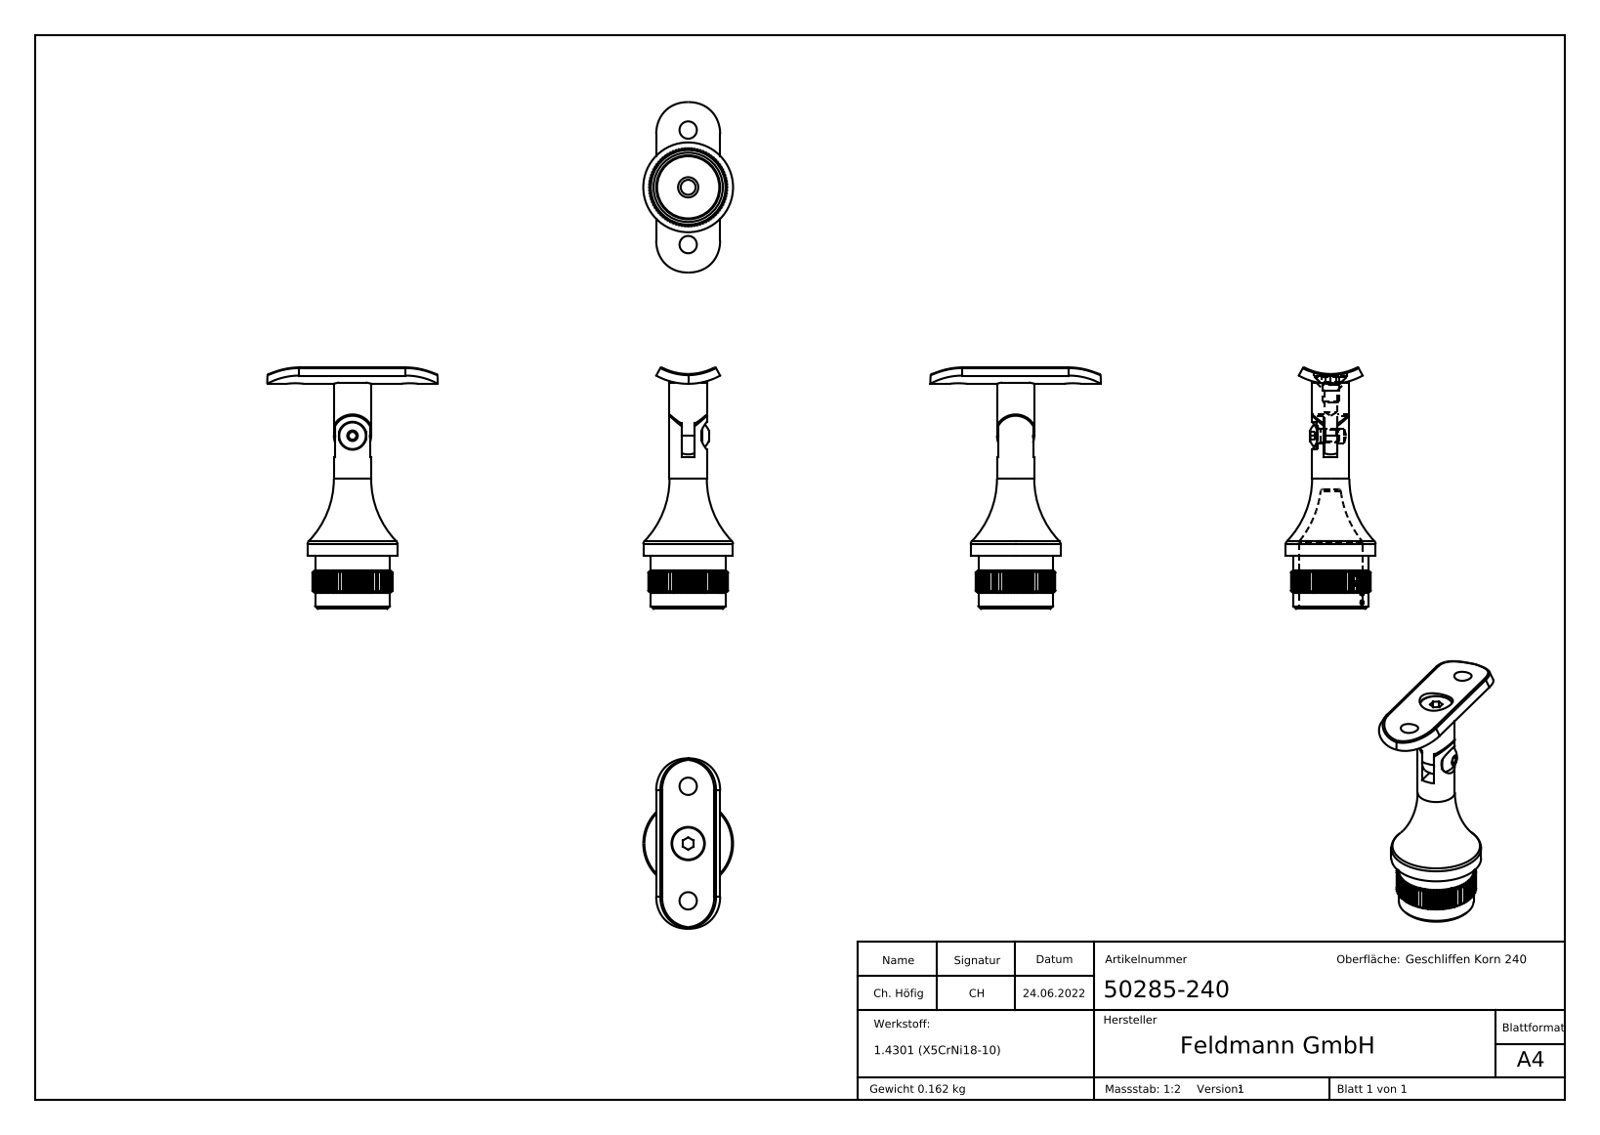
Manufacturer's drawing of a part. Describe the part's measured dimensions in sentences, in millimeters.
The part is named "5028x-240 Teil3_5028x-240 Teil3; 50285-240; DIN 7380_DIN 7380 M5x8; DIN 7991 Konfig_DIN 7991 M6x10 (+2 more)". Its 3-D file was written by "SolidWorks 2018 (CONFIG_CONTROL_DESIGN)". It is 5 solids with 773 faces: 308 planar, 144 cylindrical and 321 other. Overall it measures 90.65 by 64 by 33.7 millimeters. Its volume is 20 477 cubic millimeters and its surface area 14 967 square millimeters. Round holes: 2 of diameter 6.5, 1 of diameter 4.2, 1 of diameter 5, 1 of diameter 5.5, 1 of diameter 8.1, 1 of diameter 10.5, 1 of diameter 12.5, 1 of diameter 24. Round bosses or shafts: 1 of diameter 33.7, 1 of diameter 28, 1 of diameter 14, 1 of diameter 12, 1 of diameter 10, 1 of diameter 6, 1 of diameter 5. Partial cylindrical surfaces (rounded edges, fillets, slot ends): 4 of radius 12, 2 of radius 0.5, 1 of radius 7.1, 1 of radius 7.5, 1 of radius 8, 1 of radius 12.1, 1 of radius 14.93, 1 of radius 21.2. The main face-to-face distances are 14, 5.05, 2.35, 14.02, 5.1, 5, 65, 13.98, 7.45, 7.4. The hole center spacings are 21.5, 43.
